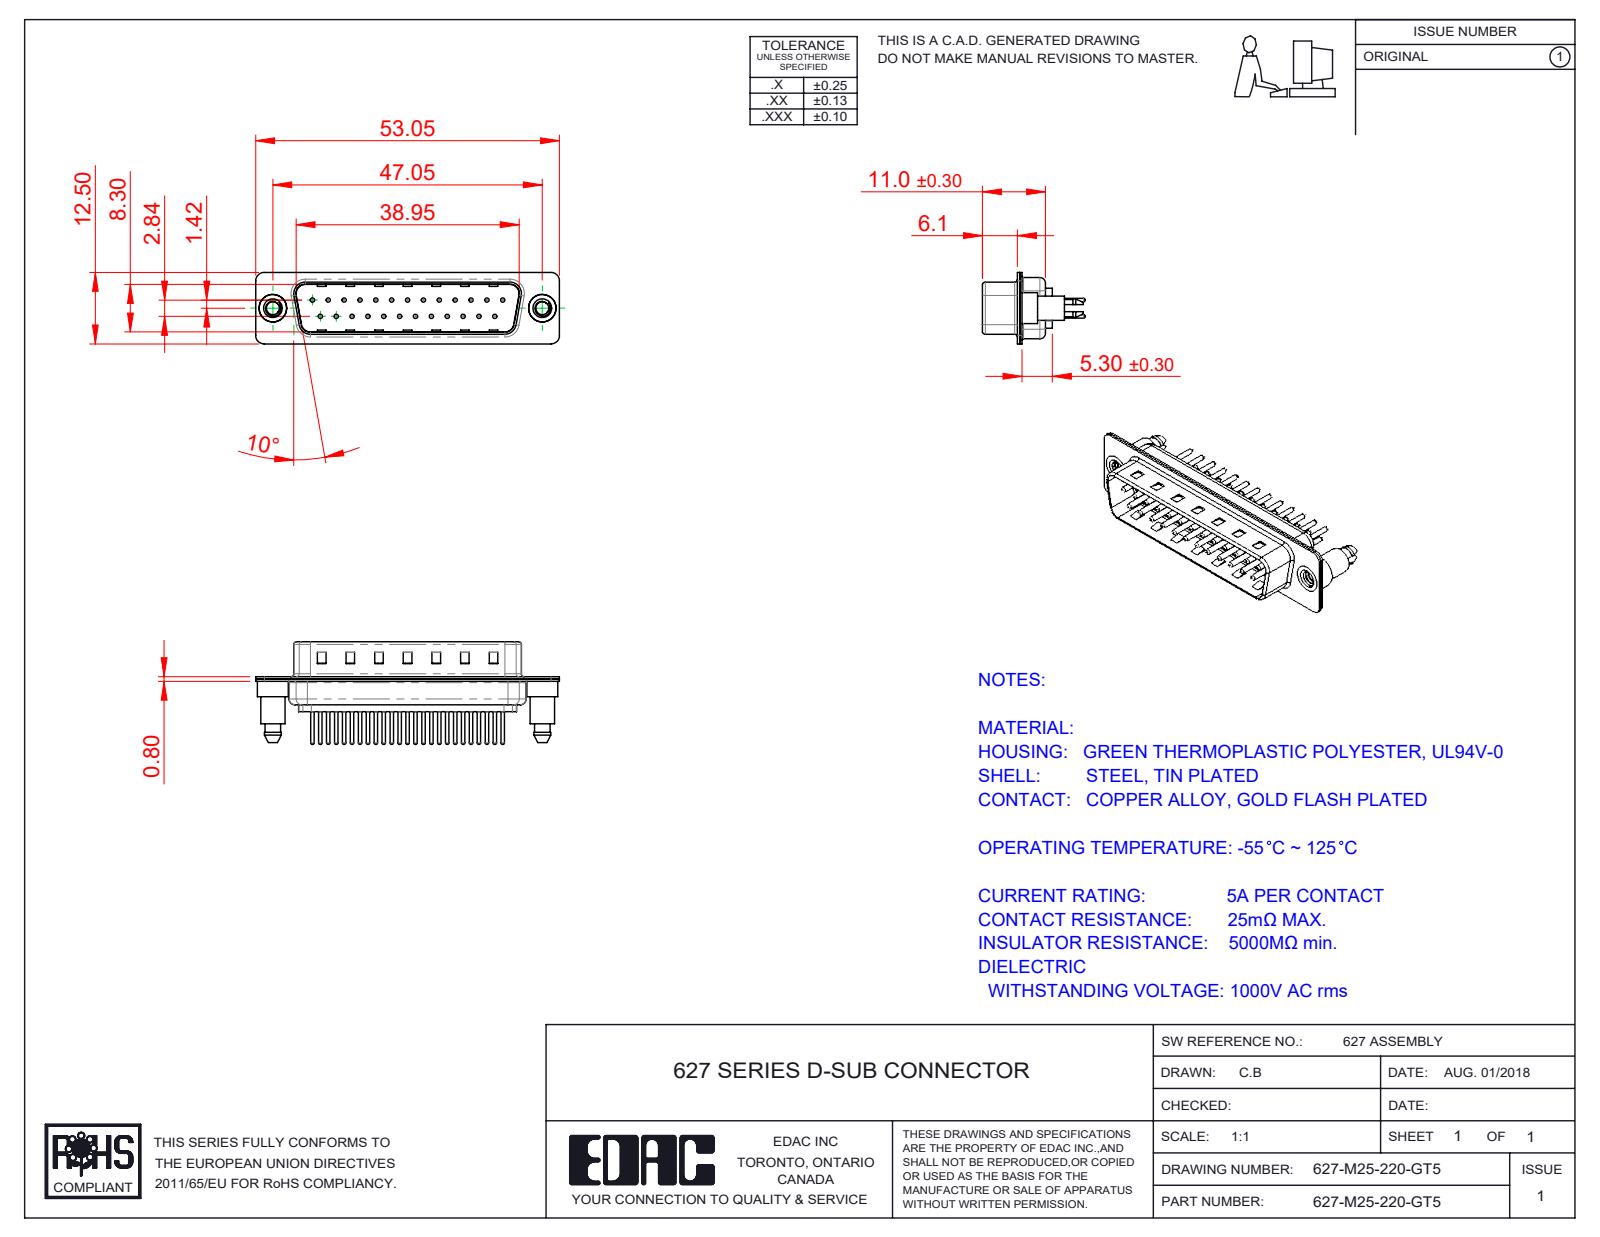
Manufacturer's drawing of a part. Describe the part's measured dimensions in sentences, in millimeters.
The part is named "627M Contact Row 1_20; 627M Contact Row 2_20; 627-M25-220-GT5; 627M Shell Rear_25 Contacts (+3 more)". Its 3-D file was written by "SolidWorks 2020 (CONFIG_CONTROL_DESIGN)". It is 30 solids with 1351 faces: 362 planar, 519 cylindrical and 470 other. Overall it measures 53.05 by 17.9 by 12.5 millimeters. Its volume is 2 853 cubic millimeters and its surface area 7 176 square millimeters. Round holes: 25 of diameter 0.75, 25 of diameter 1.6, 25 of diameter 2, 2 of diameter 2.26, 2 of diameter 4, 2 of diameter 4.8. Round bosses or shafts: 25 of diameter 1.5, 25 of diameter 0.6, 2 of diameter 5.4, 2 of diameter 4.9, 2 of diameter 4.25. Partial cylindrical surfaces (rounded edges, fillets, slot ends): 18 of radius 1.5, 12 of radius 2, 10 of radius 1.6, 8 of radius 0.5, 4 of radius 0.25, 4 of radius 0.6, 4 of radius 0.65, 4 of radius 0.9. The main face-to-face distances are 0.4, 0.8, 9.5, 9.1, 8.7, 9.9, 1.2, 6.1, 5.7, 0.75. The hole center spacings are 3.16, 2.77, 5.54, 8.31, 11.08, 13.85, 16.62, 5.03.
